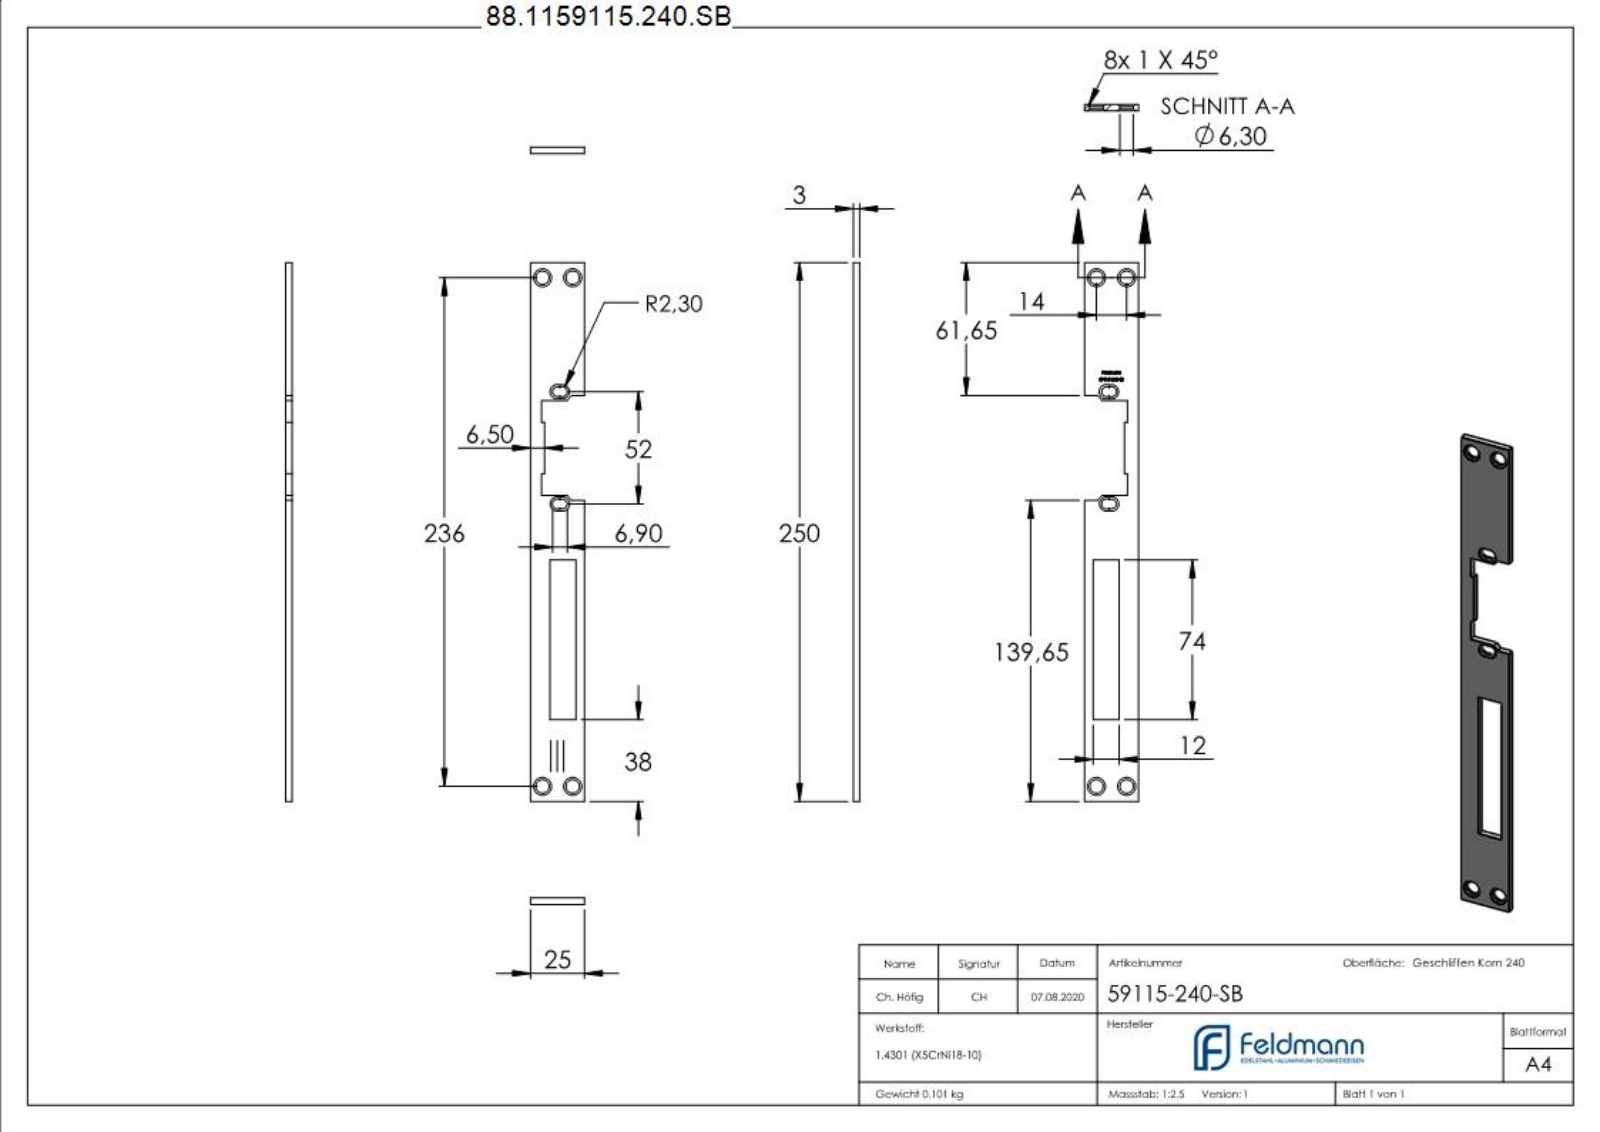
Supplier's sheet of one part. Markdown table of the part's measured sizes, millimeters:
| quantity | value |
| --- | --- |
| part name | 59115-240-SB |
| STEP written by | SolidWorks 2018 (CONFIG_CONTROL_DESIGN) |
| units | millimeters |
| bodies | 1 solid, 323 faces (169 planar, 14 cylindrical, 140 other) |
| overall size | 250 × 25 × 3 |
| volume | 12 790 mm³ |
| surface area | 11 143 mm² |
| round holes (diameter × count) | 6.3 × 4 |
| partial cylindrical surfaces (radius × count) | 2.3 × 4 |
| main face-to-face distances | 3, 25, 4, 16, 9, 21, 12, 74, 250, 6.5 |
| hole center spacings | 14, 236, 236.41 |
